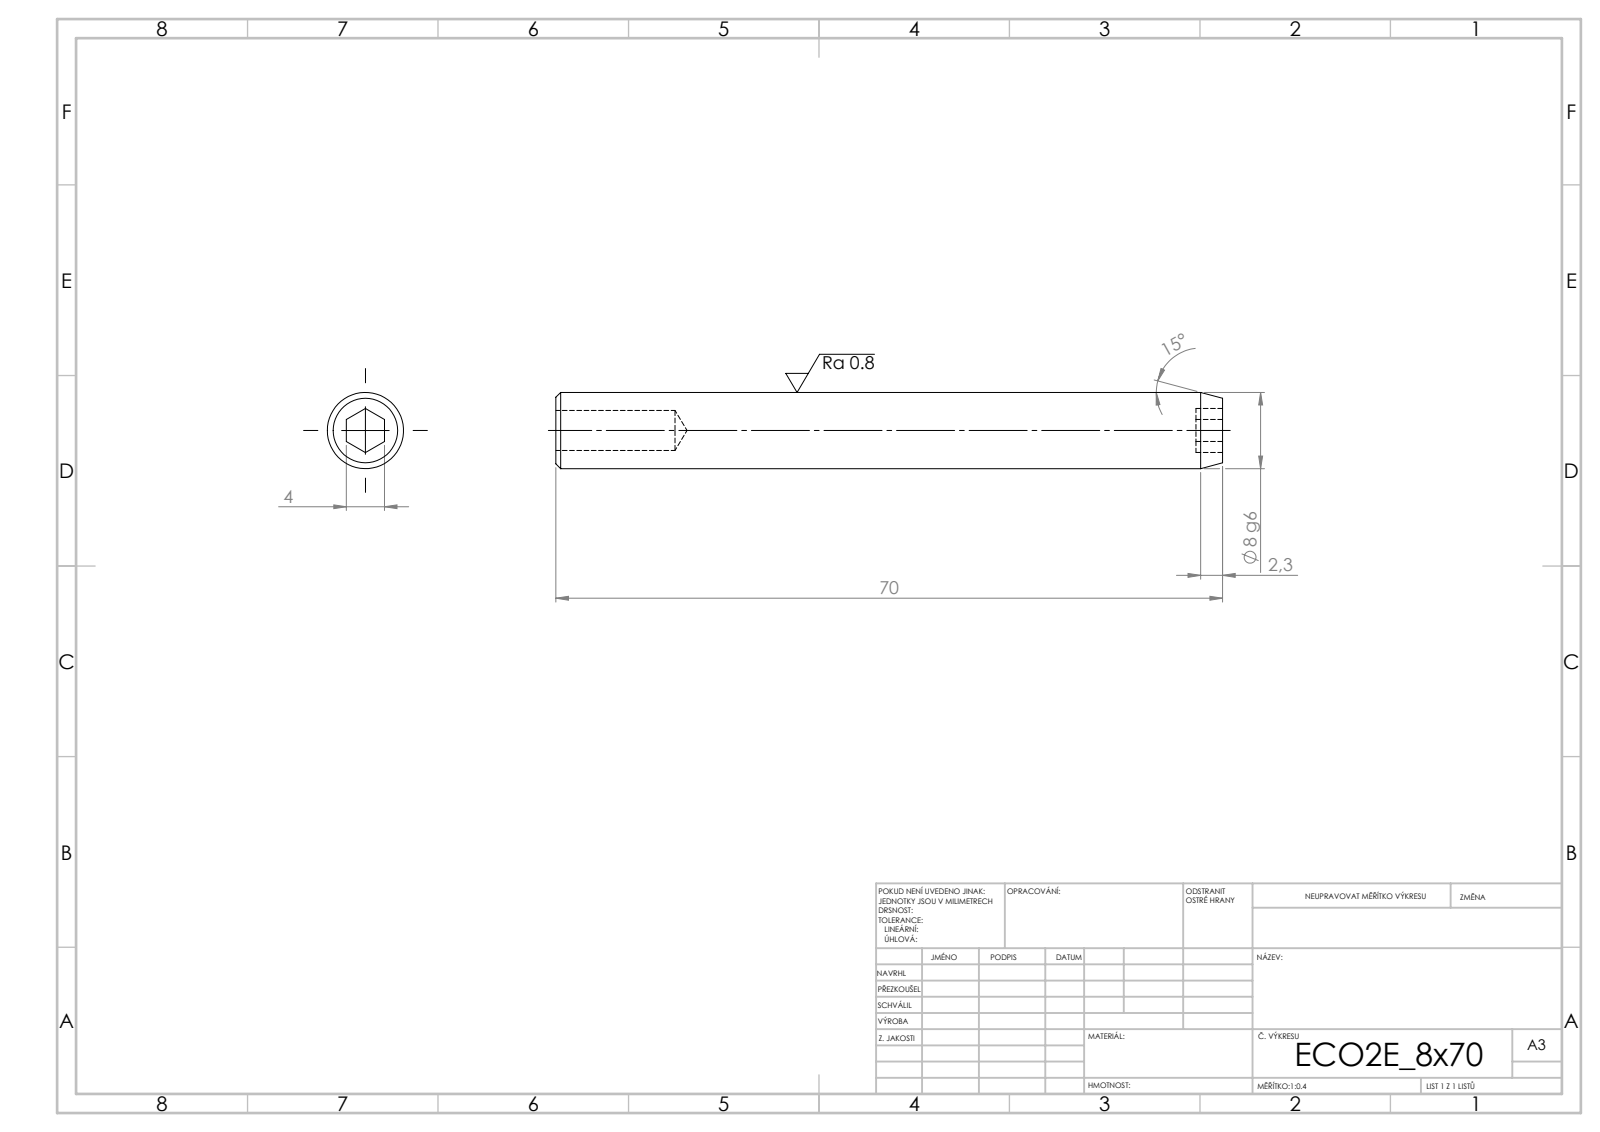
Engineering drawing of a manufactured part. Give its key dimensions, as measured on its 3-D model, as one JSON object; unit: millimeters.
{"step_written_by": "SolidWorks 2019 (CONFIG_CONTROL_DESIGN)", "units": "millimeters", "bodies": {"solids": 1, "faces": 19, "planar": 9, "cylindrical": 4, "other": 6}, "overall_size": [70, 8, 8], "volume_mm3": 3281, "surface_area_mm2": 2041, "round_holes": [[4.2, 1]], "round_bosses_or_shafts": [[8, 1]], "face_to_face_distances": [70, 4, 2.8, 67.2]}
